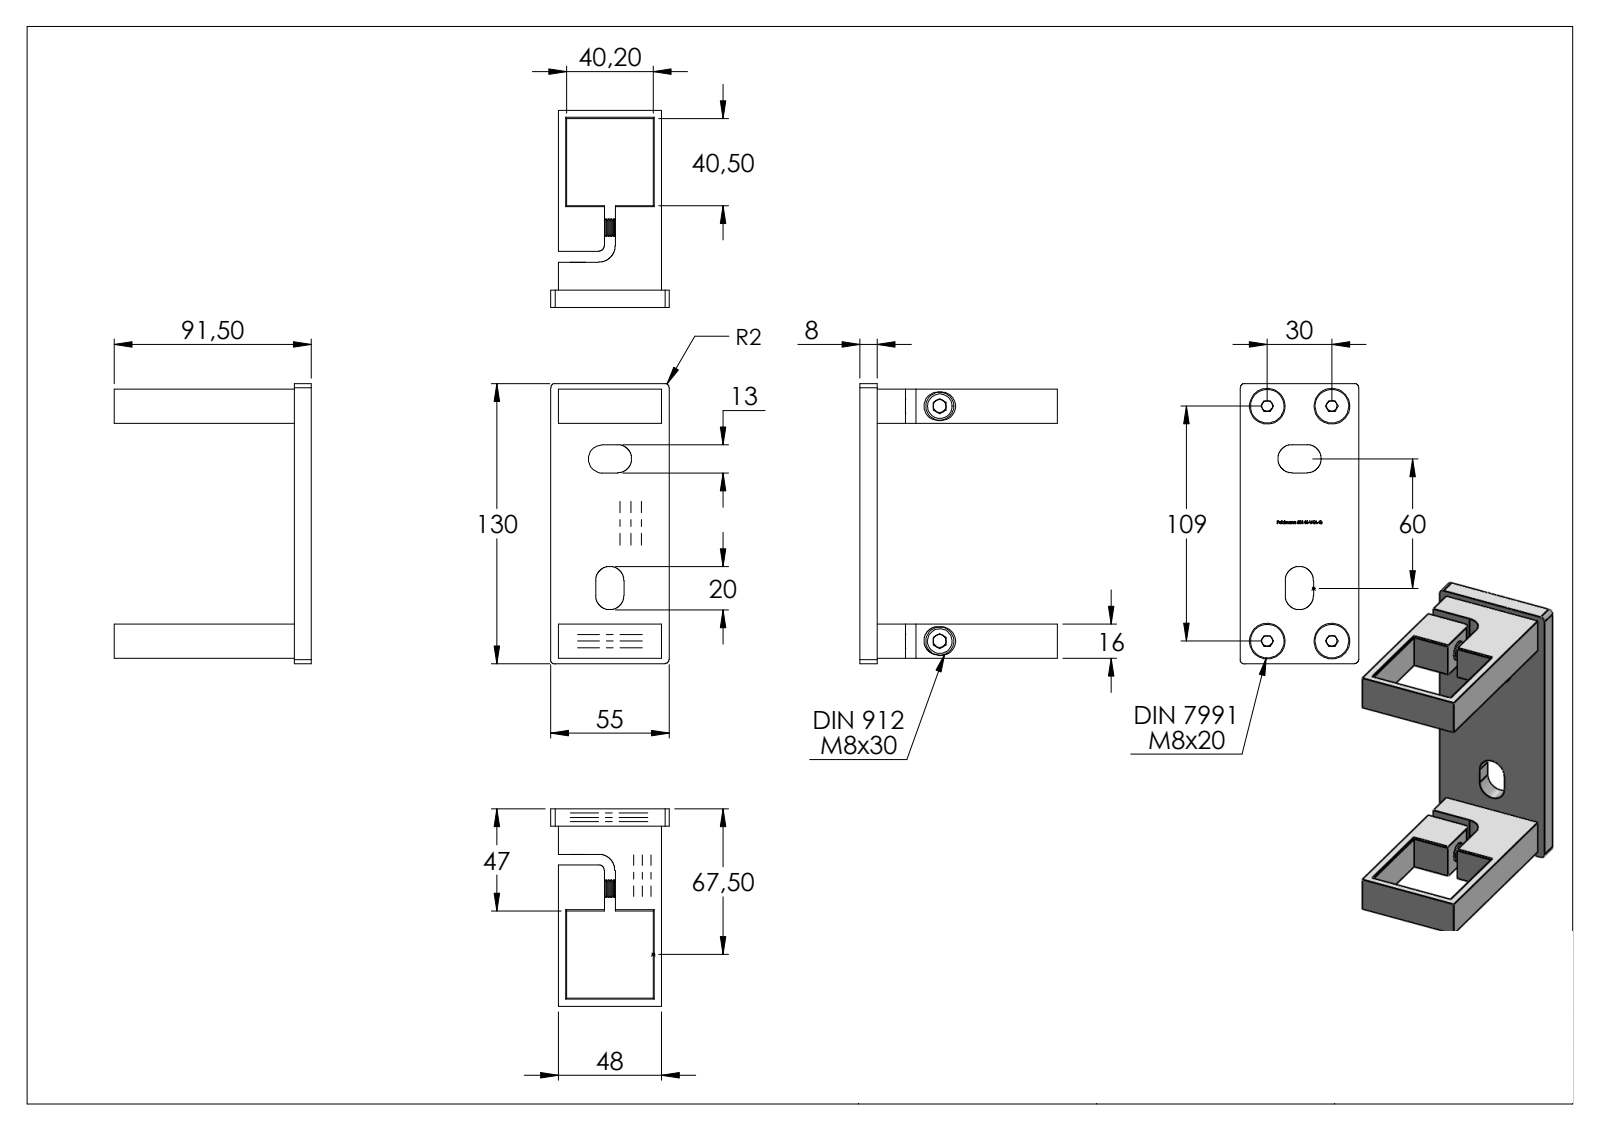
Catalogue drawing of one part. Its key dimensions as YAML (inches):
part_name: "socket countersunk head screw_din_DIN 7991 - M8 x 20 --- 20S; 50138-240P Konfig_50146-V4A-Q Teil1; 50146-V4A-Q; socket head cap screw_din_DIN 912 M8 x 30 --- 30S (+1 more)"
step_written_by: "SolidWorks 2015 (CONFIG_CONTROL_DESIGN)"
units: inches
bodies: {solids: 9, faces: 1100, planar: 327, cylindrical: 253, other: 520}
overall_size: [5.118, 3.602, 2.165]
volume: 6.919
surface_area: 84.73
round_holes:
  - {diameter: 0.268, count: 6}
  - {diameter: 0.335, count: 4}
  - {diameter: 0.65, count: 4}
  - {diameter: 0.354, count: 2}
round_bosses_or_shafts:
  - {diameter: 0.315, count: 6}
  - {diameter: 0.613, count: 4}
  - {diameter: 0.512, count: 2}
partial_cylinders:
  - {radius: 0.059, count: 4}
  - {radius: 0.256, count: 4}
  - {radius: 0.266, count: 4}
  - {radius: 0.039, count: 2}
  - {radius: 0.098, count: 1}
  - {radius: 0.197, count: 1}
face_to_face_distances: [0.315, 4.291, 0.63, 1.89, 0.148, 1.742, 0.138, 0.118, 0.285, 1.88]
hole_center_spacings: [4.291, 1.181, 4.451]
